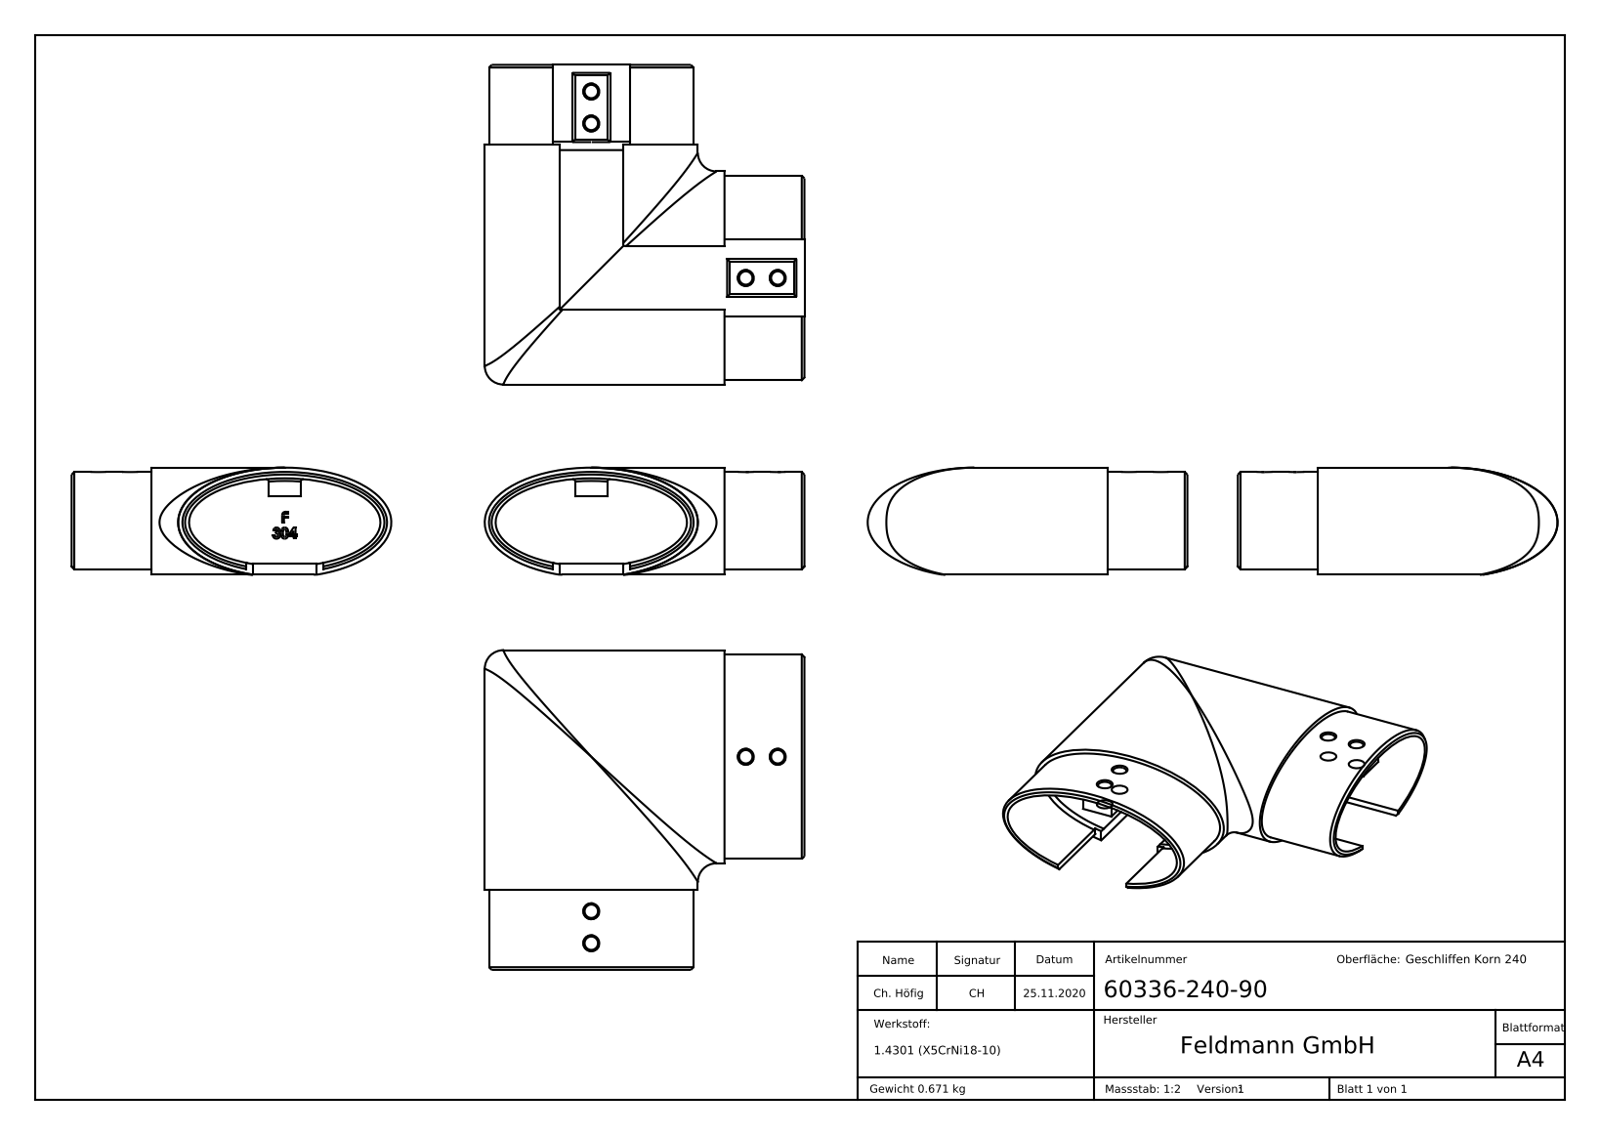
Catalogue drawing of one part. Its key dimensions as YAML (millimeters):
part_name: "60336-240-90"
step_written_by: "SolidWorks 2018 (CONFIG_CONTROL_DESIGN)"
units: millimeters
bodies: {solids: 1, faces: 395, planar: 179, cylindrical: 12, other: 204}
overall_size: [120, 120, 40.23]
volume: 86524
surface_area: 53102
round_holes:
  - {diameter: 5, count: 4}
partial_cylinders:
  - {radius: 1, count: 4}
face_to_face_distances: [6, 18, 62, 24, 92, 30, 38, 68, 8.5, 2.5]
hole_center_spacings: [12, 90.91, 82.02, 98.99]
